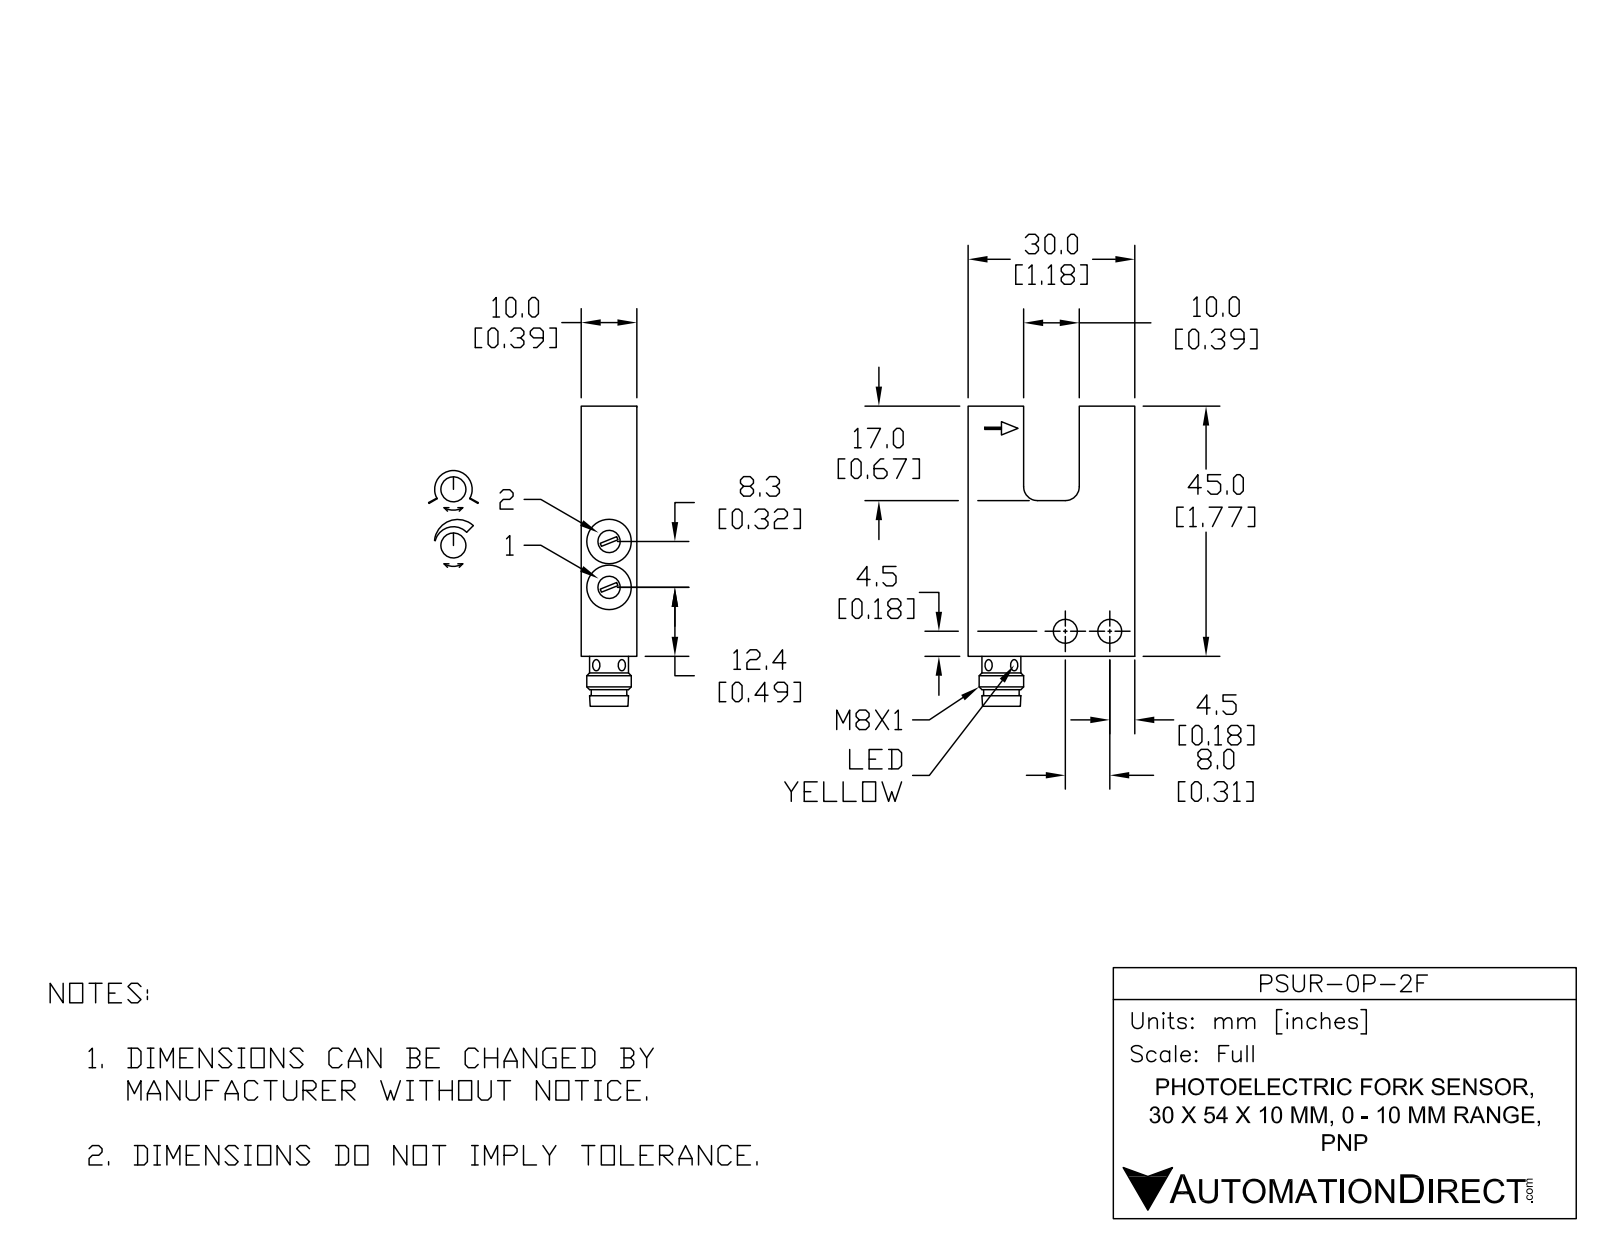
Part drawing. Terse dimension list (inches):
name: PSUR-0P-2F
written by: SolidWorks 2016 (AUTOMOTIVE_DESIGN)
unit: in
bodies: 1 solid, 75 faces (35 planar, 34 cylindrical, 6 other)
size: 2.126 × 1.181 × 0.394
volume: 0.716 in³; area: 7.329 in²
holes: 2× ⌀0.079, 2× ⌀0.157, 2× ⌀0.169, 2× ⌀0.315, 1× ⌀0.228
bosses: 1× ⌀0.315, 1× ⌀0.267
rounds: 2× R0.063, 2× R0.098
face distances: 0.394, 1.181, 0.787, 1.772, 0.39, 1.177, 0.783, 0.669, 1.102, 0.157
hole spacings: 0.315, 0.325
